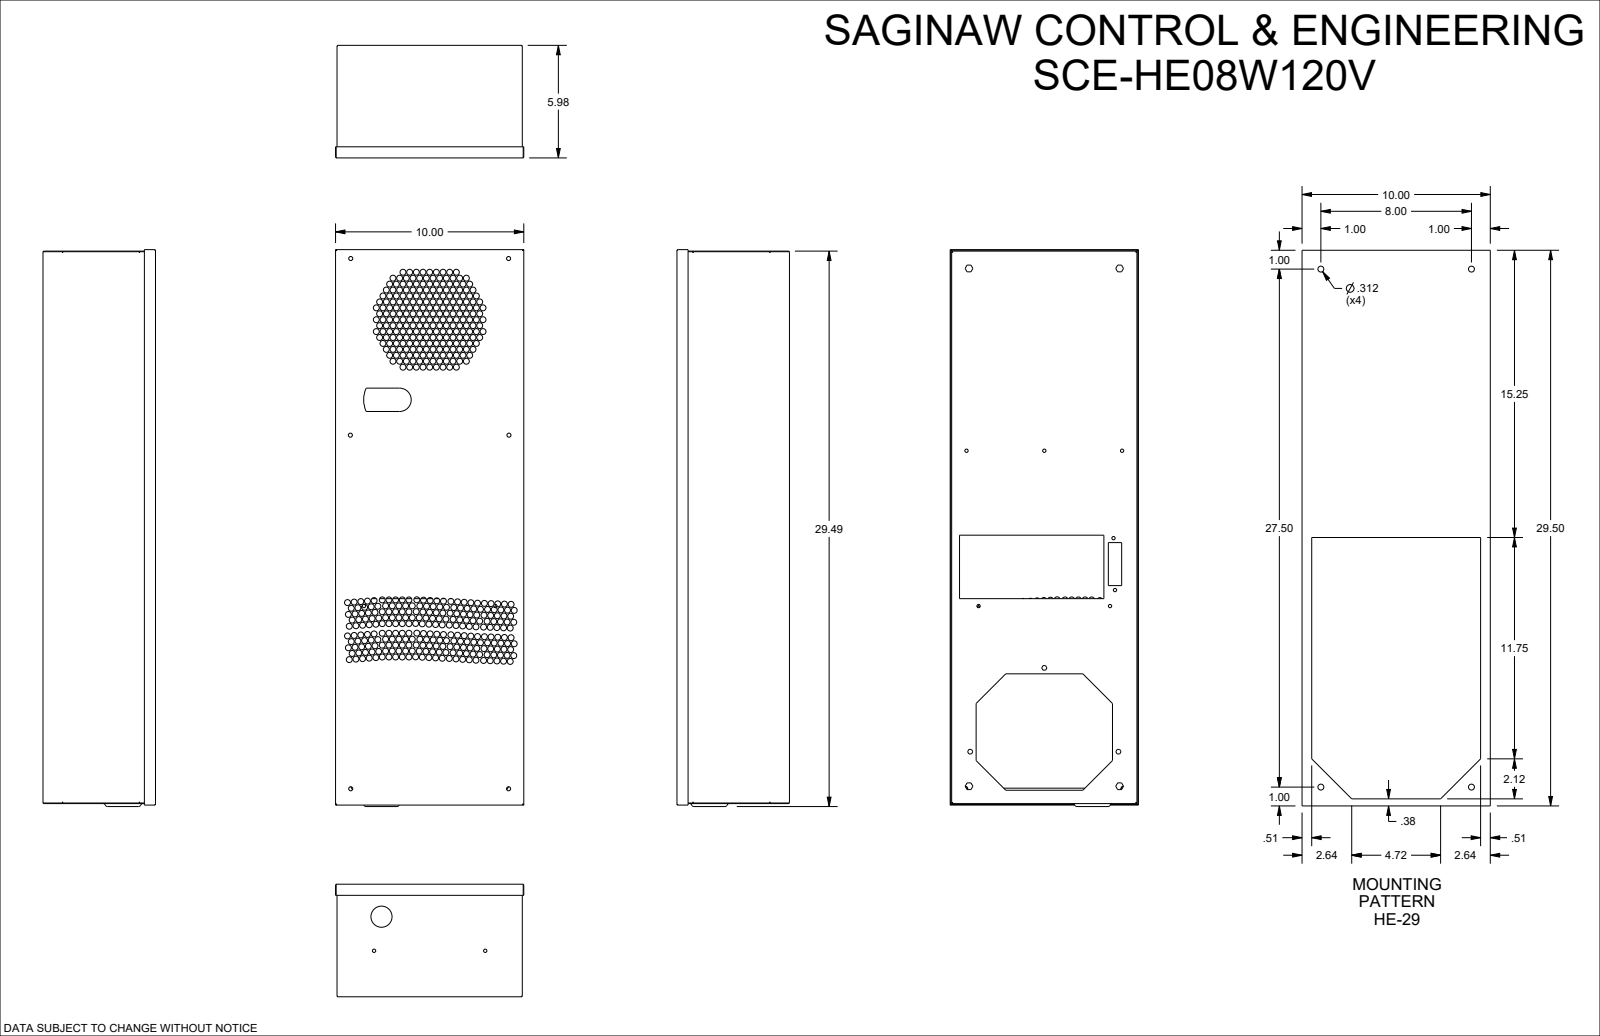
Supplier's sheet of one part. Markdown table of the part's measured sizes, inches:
| quantity | value |
| --- | --- |
| part name | SCE-HE08W120V |
| STEP written by | SolidWorks 2023 (AUTOMOTIVE_DESIGN) |
| units | inches |
| bodies | 1 solid, 1111 faces (591 planar, 517 cylindrical, 3 other) |
| overall size | 29.567 × 10 × 6.105 |
| volume | 1 726 in³ |
| surface area | 1 073 in² |
| round holes (diameter × count) | 0.315 × 491, 0.177 × 7, 0.217 × 6, 1.122 × 1 |
| partial cylindrical surfaces (radius × count) | 0.063 × 8, 0.6 × 1, 0.62 × 1, 1.477 × 1, 1.497 × 1 |
| main face-to-face distances | 5.976, 9.843, 0.031, 5.945, 29.331, 0.079, 5.913, 9.921, 10, 29.409 |
| hole center spacings | 0.354, 0.709, 0.723, 1.063, 0.948, 1.235, 1.417, 0.63 |
